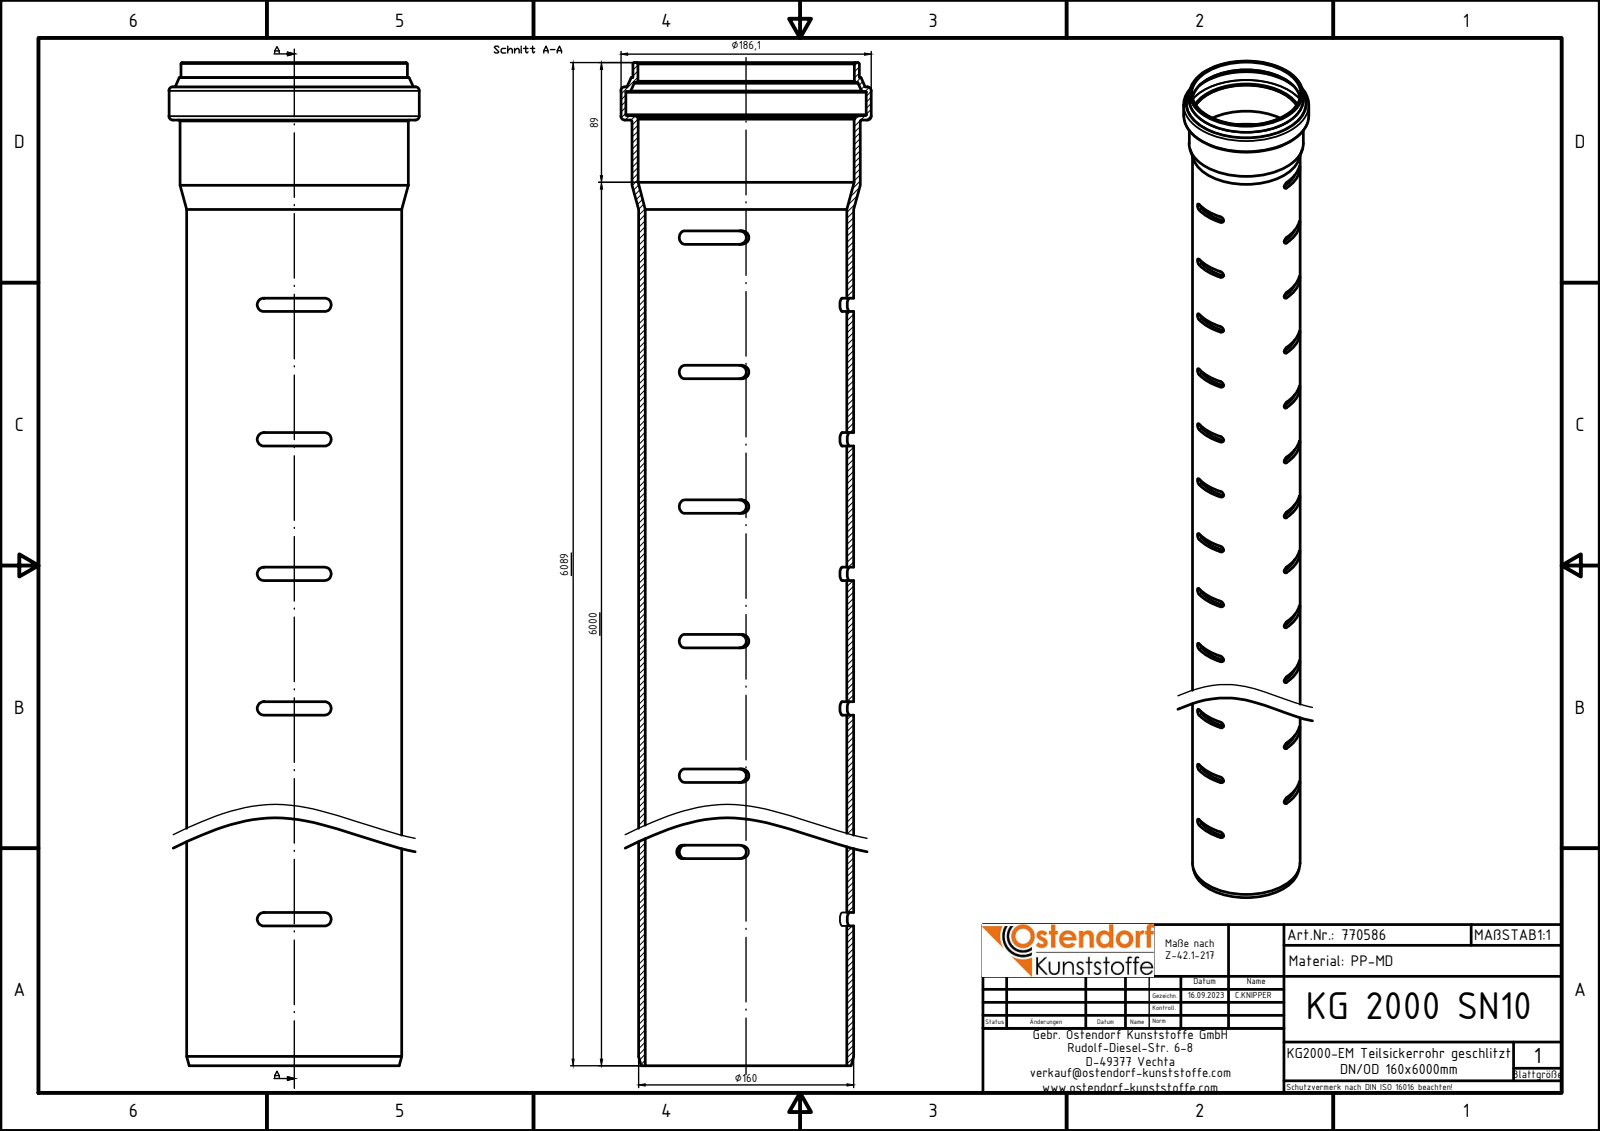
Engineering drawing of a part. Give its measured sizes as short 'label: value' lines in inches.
name: 770586z
written by: Autodesk Inventor 2024 (AUTOMOTIVE_DESIGN)
unit: in
bodies: 1 solid, 745 faces (360 planar, 363 cylindrical, 22 other)
size: 239.724 × 7.327 × 7.327
volume: 887.9 in³; area: 9 105 in²
holes: 1× ⌀5.9, 1× ⌀6.323, 1× ⌀6.339, 1× ⌀7.035
bosses: 1× ⌀7.327, 1× ⌀6.677, 1× ⌀6.63, 1× ⌀6.299
rounds: 354× R0.197
face distances: 3.937, 7.874, 11.811, 15.748, 19.685, 23.622, 27.559, 31.496, 35.433, 39.37
